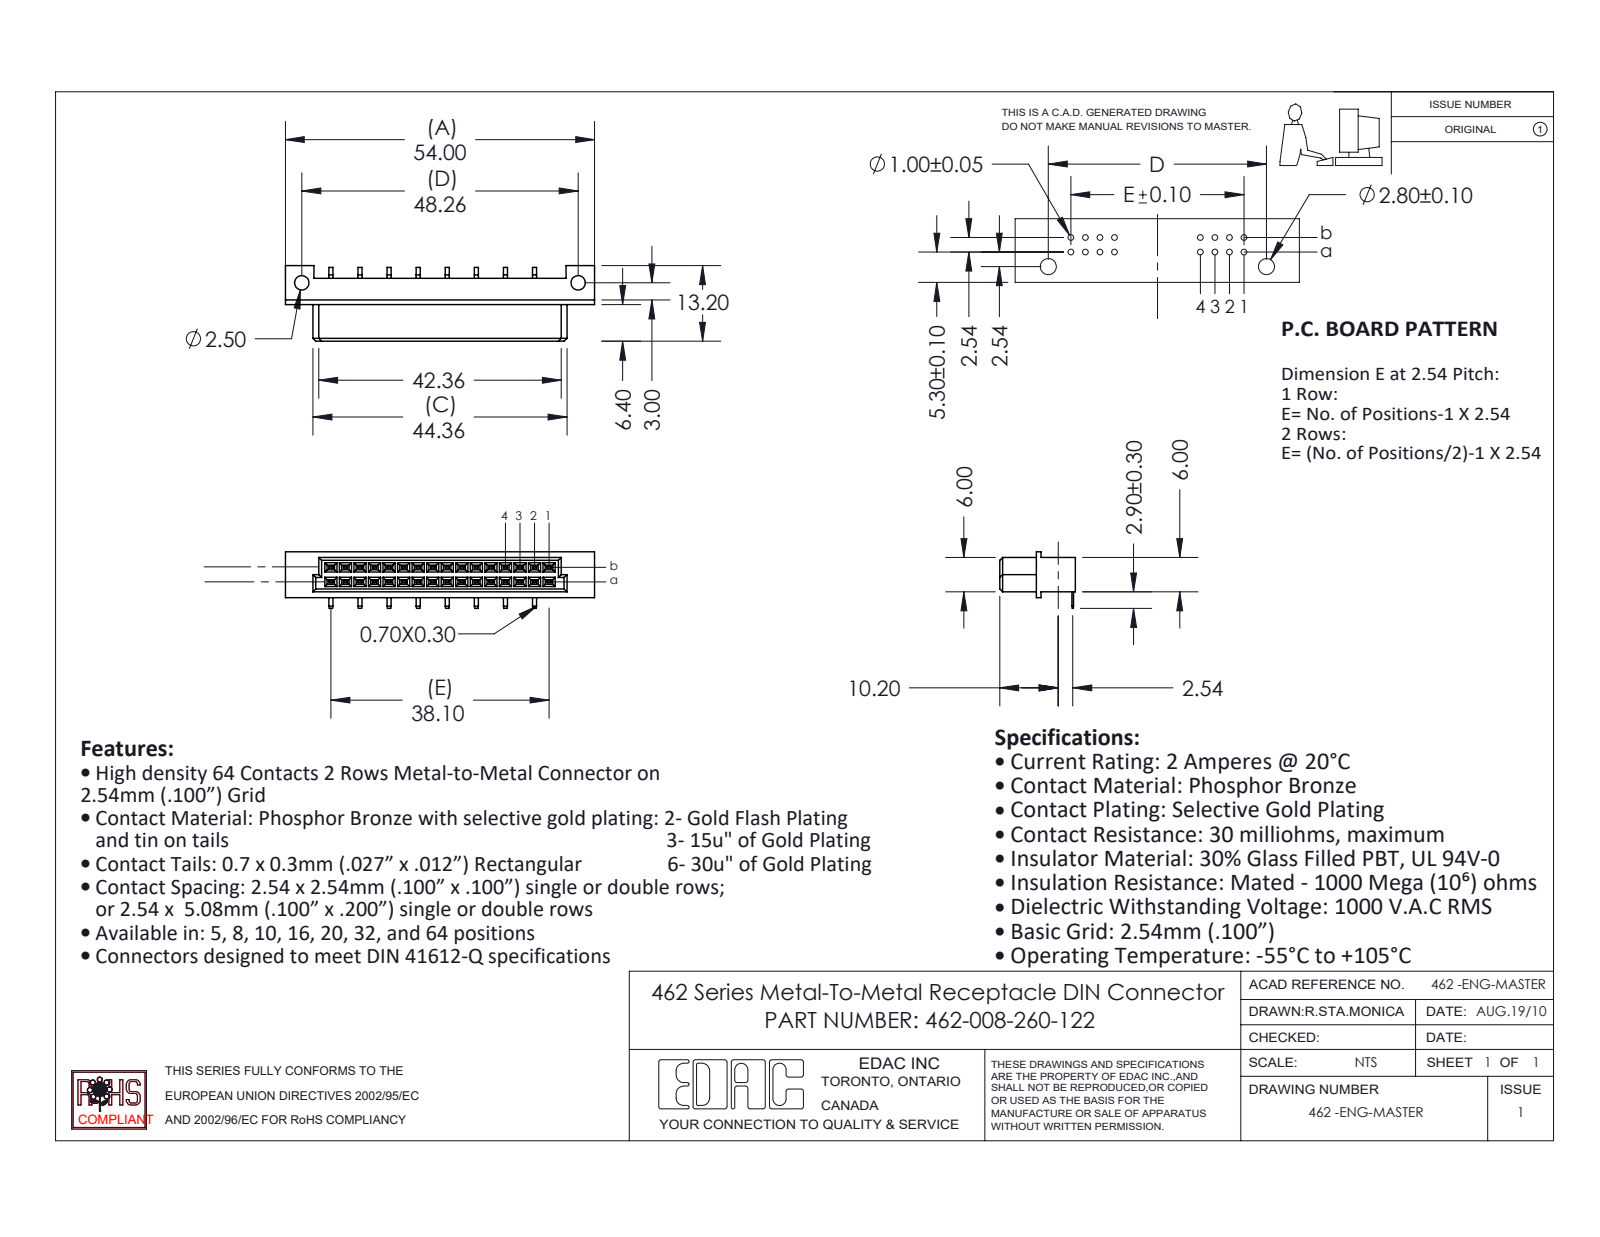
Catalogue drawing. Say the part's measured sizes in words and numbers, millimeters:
The part is named "462-290-1; 462-008-260-122; 462 Part_32". Its 3-D file was written by "SolidWorks 2020 (CONFIG_CONTROL_DESIGN)". It is 9 solids with 563 faces: 543 planar, 20 cylindrical and 0 other. Overall it measures 54 by 13.2 by 9.9 millimeters. Its volume is 3 056 cubic millimeters and its surface area 3 476 square millimeters. Round holes: 2 of diameter 2.5. Partial cylindrical surfaces (rounded edges, fillets, slot ends): 1 of radius 1.02, 1 of radius 1.32. The main face-to-face distances are 6, 2.54, 0.81, 4.6, 1.32, 2.13, 3.86, 4.67, 3.35, 4.68. The hole center spacings are 48.26.
